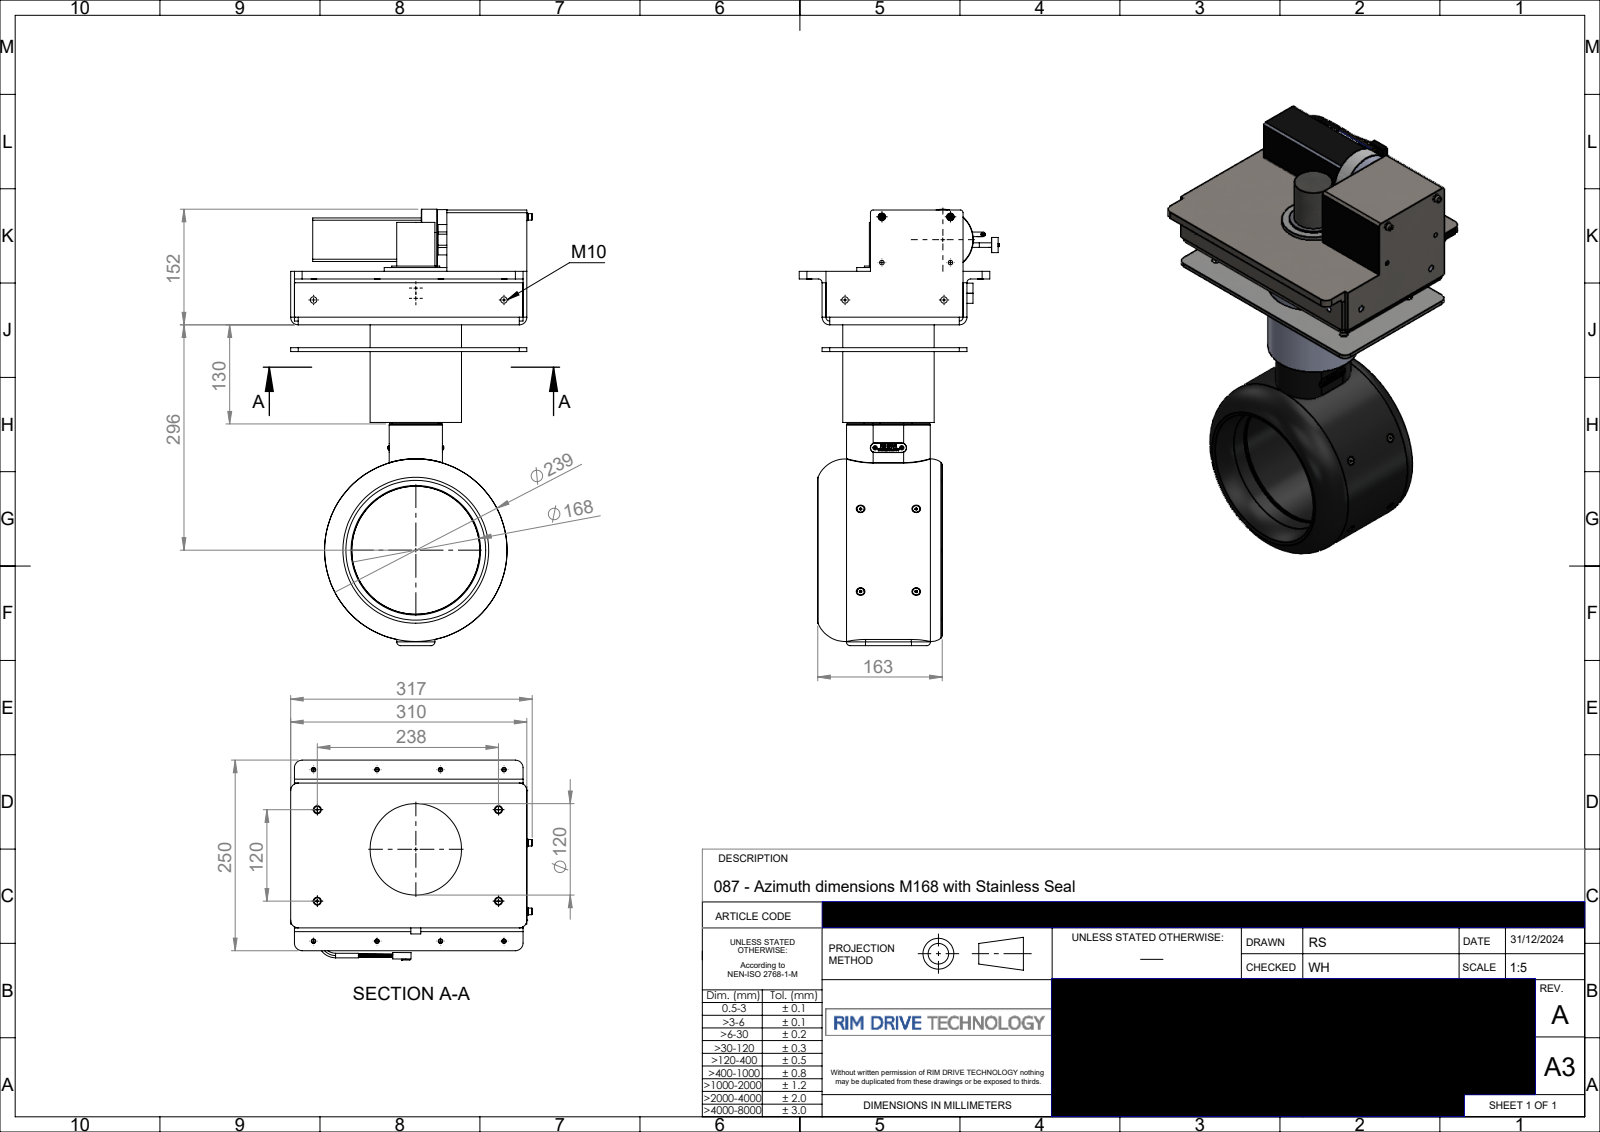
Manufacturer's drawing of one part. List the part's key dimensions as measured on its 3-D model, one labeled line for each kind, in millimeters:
Part name (STEP PRODUCT): P-087-030-rev-C-SSEAL-M168
STEP written by: SolidWorks 2024 (AUTOMOTIVE_DESIGN)
Units: millimetres
Bodies: 1 solid, 1146 faces (712 planar, 181 cylindrical, 253 other)
Overall size (bounding box): 572.55 × 317 × 262.71
Volume: 11 520 000 mm³ · Surface area: 721 851 mm²
Round holes (diameter × count): ⌀8.5 ×10, ⌀5.5 ×6, ⌀6 ×4, ⌀10.5 ×4, ⌀3.5 ×2, ⌀5.1 ×2, ⌀5.3 ×2, ⌀7 ×2, ⌀168 ×1
Round bosses / shafts (diameter × count): ⌀6 ×8, ⌀5 ×8, ⌀9.64 ×6, ⌀63 ×2, ⌀13 ×2, ⌀12 ×2, ⌀10 ×2, ⌀9.2 ×2
Partial cylindrical surfaces — rounded edges, fillets, slot ends (radius × count): R10 ×12, R5 ×6, R3 ×4, R25 ×3, R0.5 ×2, R1.5 ×2, R3.01 ×2, R3.5 ×2
Main face-to-face distances: 5, 105.2, 100.2, 30, 35, 70.2, 60.2, 90.2, 10, 95.2
Hole centre spacings: 73, 120, 60, 90, 108.17, 237.8, 237.81, 266.36
